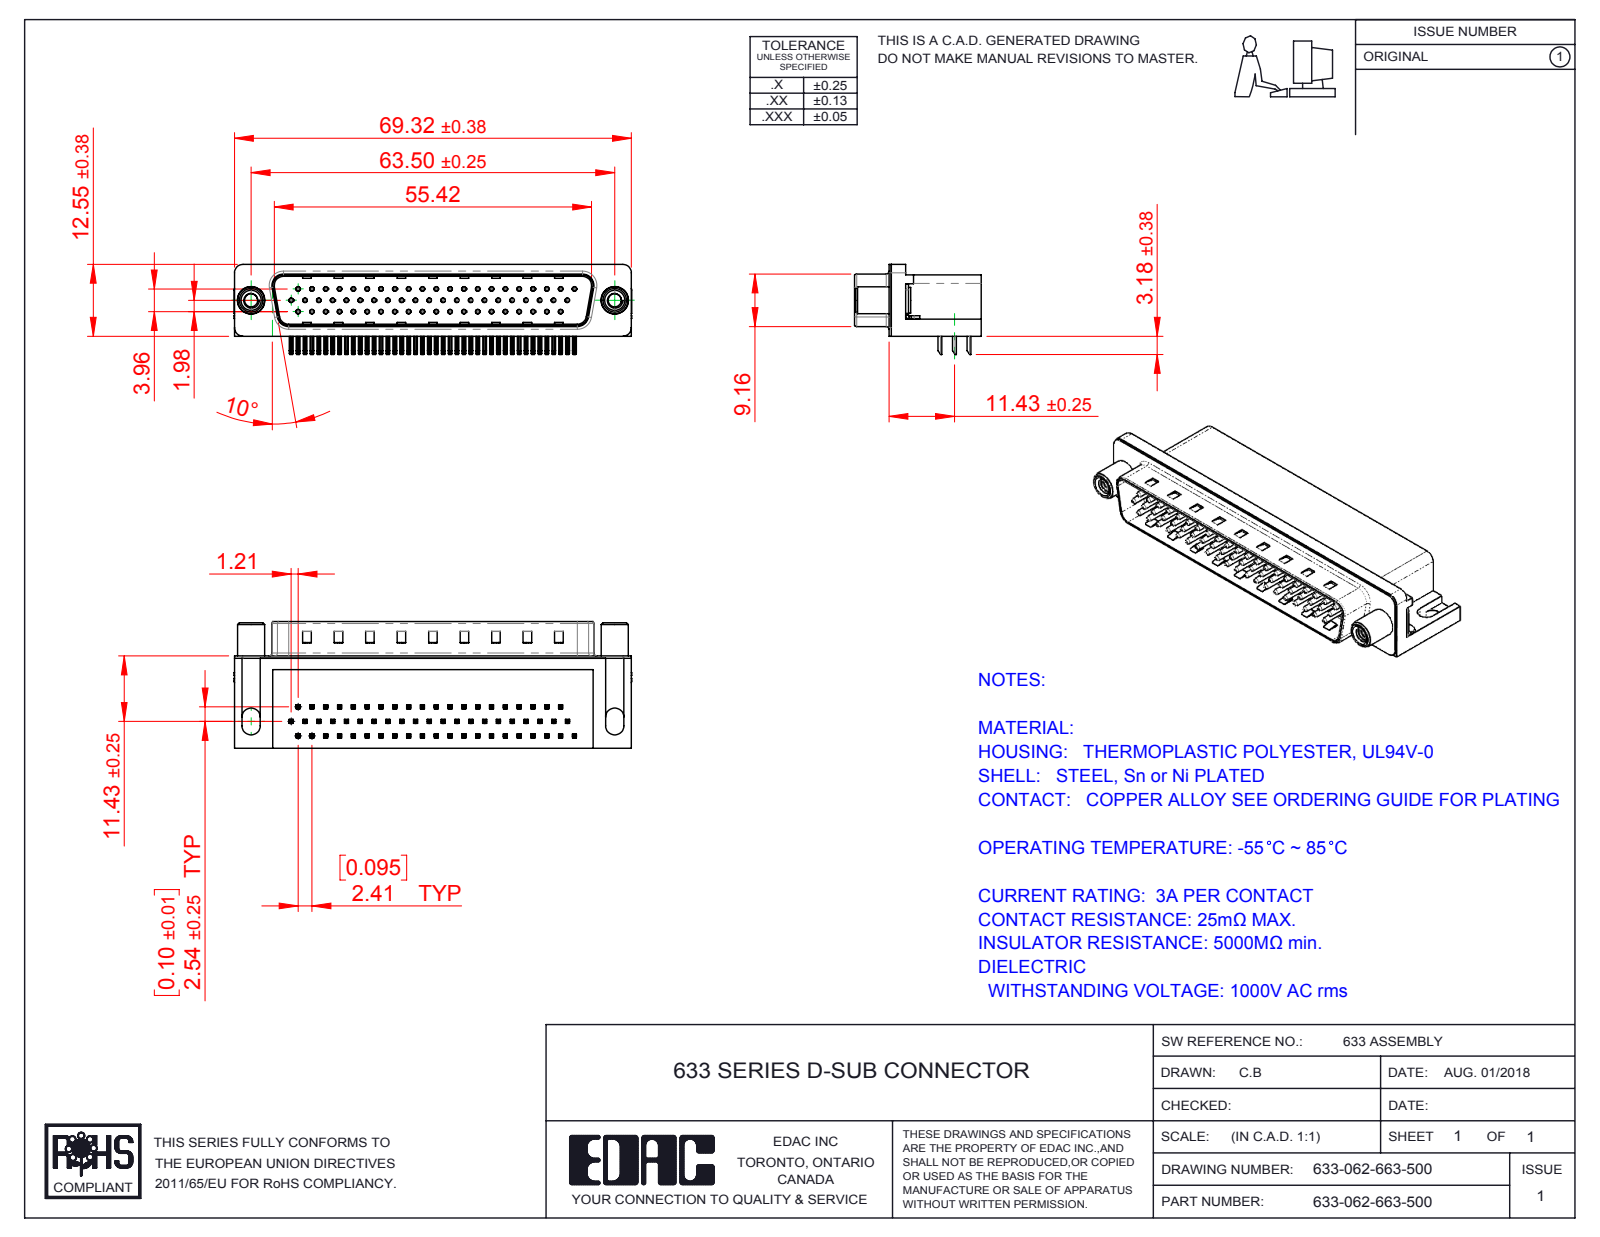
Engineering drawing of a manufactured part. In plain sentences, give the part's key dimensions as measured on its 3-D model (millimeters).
The part is named "633-062-663-500; 633 Non Board Mount; 633 Contact Bottom; 633 Shell_62 Contact (+4 more)". Its 3-D file was written by "SolidWorks 2016 (CONFIG_CONTROL_DESIGN)". It is 68 solids with 5066 faces: 3205 planar, 1446 cylindrical and 415 other. Overall it measures 69.4 by 22.1 by 15.73 millimeters. Its volume is 11 098 cubic millimeters and its surface area 13 381 square millimeters. Round holes: 62 of diameter 0.35, 62 of diameter 0.8, 2 of diameter 2.3, 2 of diameter 3.1, 2 of diameter 4, 2 of diameter 4.8, 2 of diameter 5. Round bosses or shafts: 62 of diameter 0.75, 2 of diameter 4.9, 2 of diameter 4.7, 2 of diameter 4.5, 2 of diameter 3.85. Partial cylindrical surfaces (rounded edges, fillets, slot ends): 248 of radius 0.25, 124 of radius 0.12, 16 of radius 1, 9 of radius 0.5, 8 of radius 1.6, 7 of radius 1.5, 4 of radius 0.9, 4 of radius 2. The main face-to-face distances are 0.4, 10.35, 15.7, 8.76, 2.5, 2.9, 2.54, 8.36, 2.1, 8.6. The hole center spacings are 2.41, 4.82, 7.24, 9.65, 14.48, 16.89, 4.83, 7.23.
